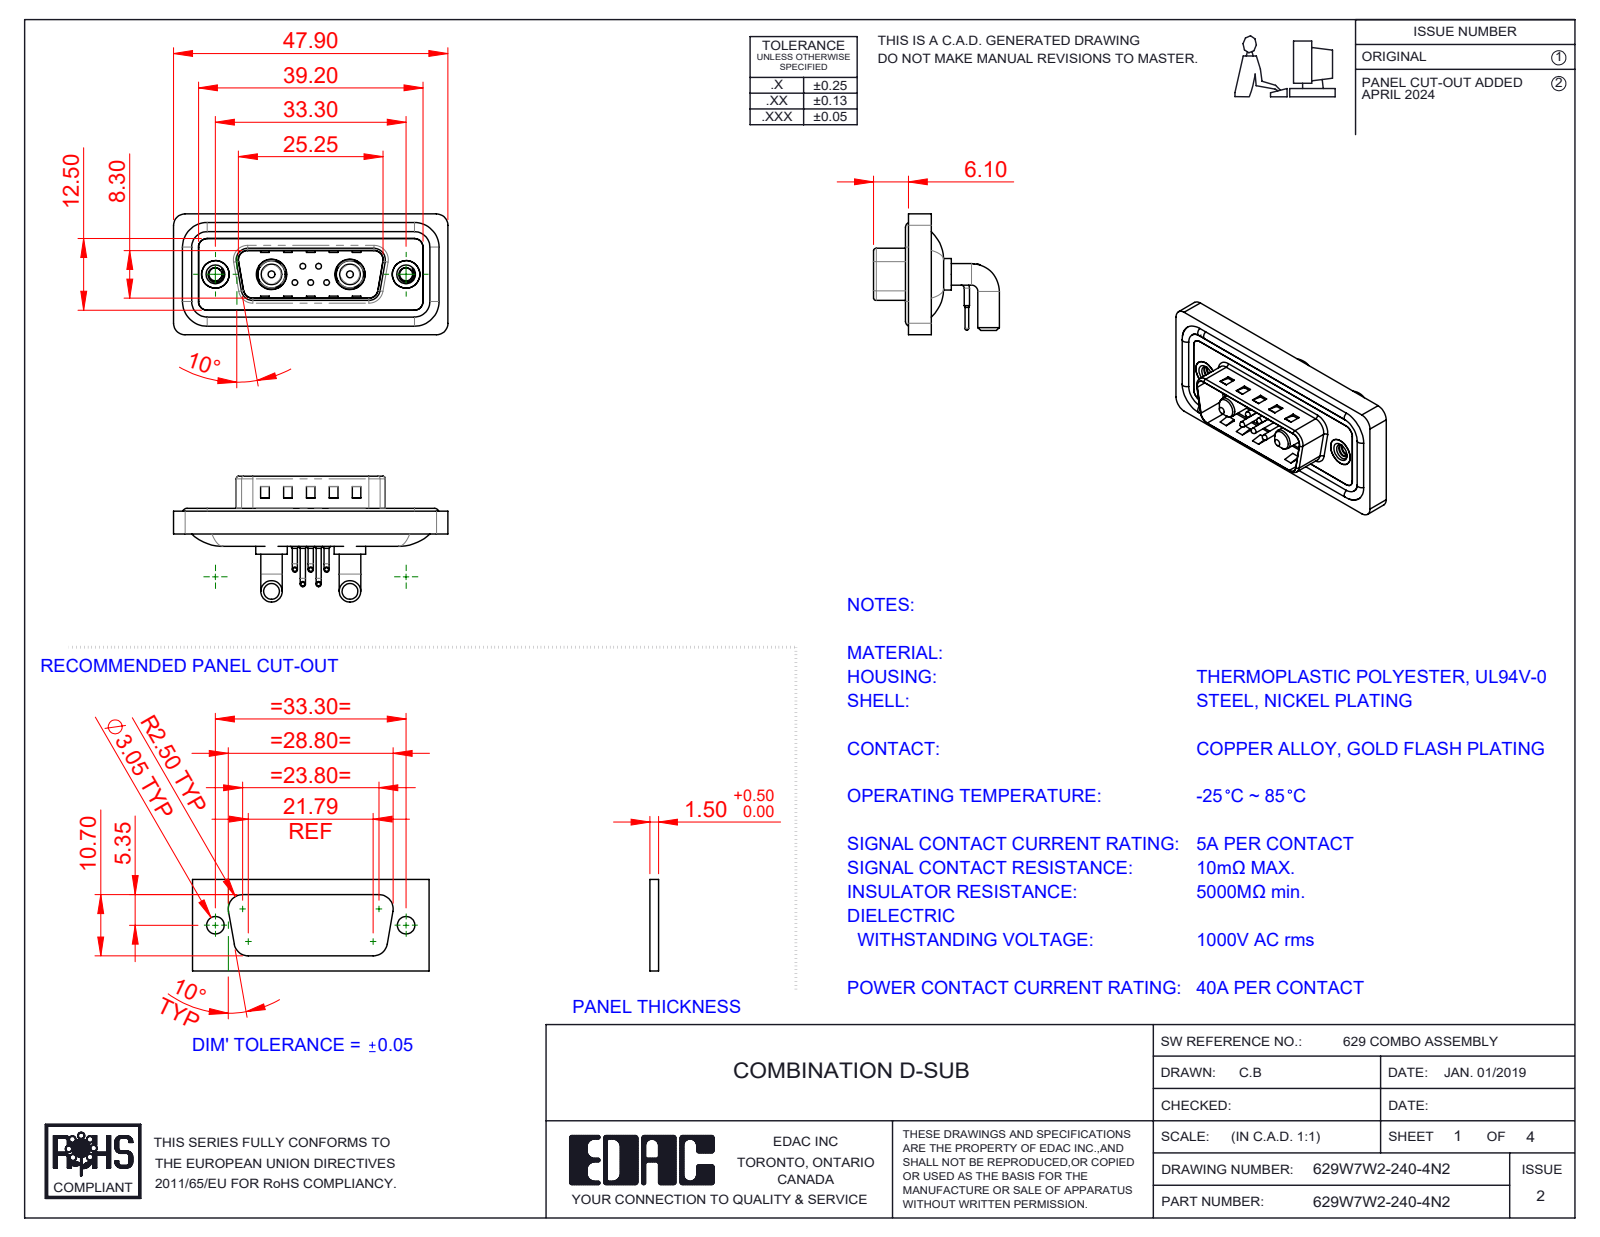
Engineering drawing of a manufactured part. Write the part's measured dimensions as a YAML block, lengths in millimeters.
part_name: "629W7W2-240-4N2; 629Combo Contact Row 1; Power Pin_40A RA; 629Combo Waterproof Housing_15 Contacts (+5 more)"
step_written_by: "SolidWorks 2023 (CONFIG_CONTROL_DESIGN)"
units: millimeters
bodies: {solids: 16, faces: 1083, planar: 517, cylindrical: 406, other: 160}
overall_size: [47.9, 21.98, 21.1]
volume: 5837
surface_area: 9229
round_holes:
  - {diameter: 0.75, count: 5}
  - {diameter: 1.6, count: 5}
  - {diameter: 2, count: 5}
  - {diameter: 2.26, count: 2}
  - {diameter: 4, count: 2}
  - {diameter: 4.8, count: 2}
  - {diameter: 4.85, count: 2}
  - {diameter: 5, count: 2}
  - {diameter: 5.3, count: 2}
round_bosses_or_shafts:
  - {diameter: 0.9, count: 10}
  - {diameter: 1.5, count: 5}
  - {diameter: 1, count: 5}
  - {diameter: 0.65, count: 5}
  - {diameter: 3.75, count: 4}
  - {diameter: 1.6, count: 4}
  - {diameter: 5.5, count: 2}
  - {diameter: 5.2, count: 2}
partial_cylinders:
  - {radius: 2, count: 20}
  - {radius: 1.5, count: 18}
  - {radius: 0.5, count: 8}
  - {radius: 1.6, count: 8}
  - {radius: 1.01, count: 5}
  - {radius: 0.25, count: 4}
  - {radius: 0.6, count: 4}
  - {radius: 0.65, count: 4}
face_to_face_distances: [0.4, 2.9, 0.8, 1.1, 2.1, 1.6, 2.5, 3.1, 4.5, 4.1]
hole_center_spacings: [3.16, 2.77, 9.8, 23.5, 4.31, 4.33, 5.03, 5.04]
